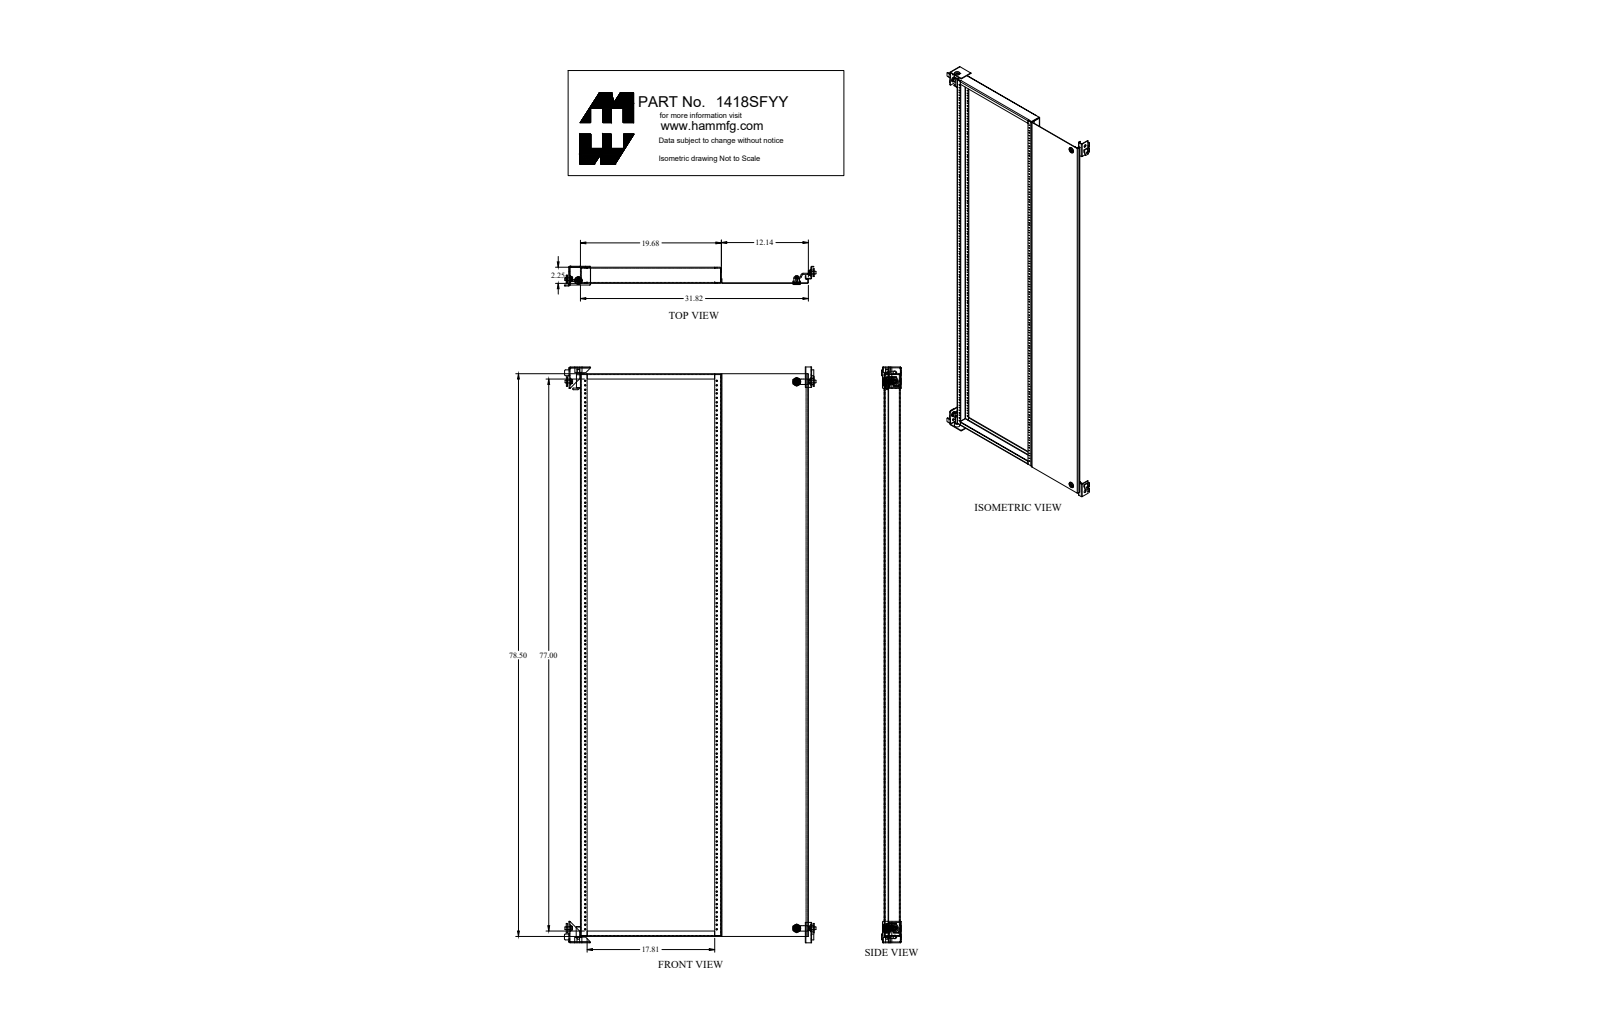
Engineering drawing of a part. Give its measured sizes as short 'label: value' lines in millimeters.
name: 1418SFYY_Default
written by: SolidWorks 2019 (CONFIG_CONTROL_DESIGN)
unit: mm
bodies: 38 solids, 1776 faces (474 planar, 1270 cylindrical, 32 other)
size: 2037.7 × 881 × 74.1
volume: 2 853 000 mm³; area: 2 446 000 mm²
holes: 264× ⌀4.5, 4× ⌀8, 4× ⌀9.7, 4× ⌀12.7, 3× ⌀11.3, 2× ⌀5.9, 2× ⌀15.9, 2× ⌀19.9, 1× ⌀9.4, 1× ⌀10.4, 1× ⌀11.3, 1× ⌀25.9
bosses: 5× ⌀25.4, 4× ⌀17.1, 3× ⌀9.5, 2× ⌀27.9, 2× ⌀13.3, 2× ⌀9, 1× ⌀22.2, 1× ⌀15
rounds: 12× R1.5, 12× R4.7, 11× R3.2, 8× R5.6, 6× R0.8, 6× R0.9, 6× R2.7, 2× R3.8
face distances: 1.8, 3.2, 3.2, 54, 496.6, 493.5, 496.6, 499.8, 1.3, 52.1
hole spacings: 44.5, 88.9, 133.4, 177.8, 222.3, 266.7, 15.9, 15.9
